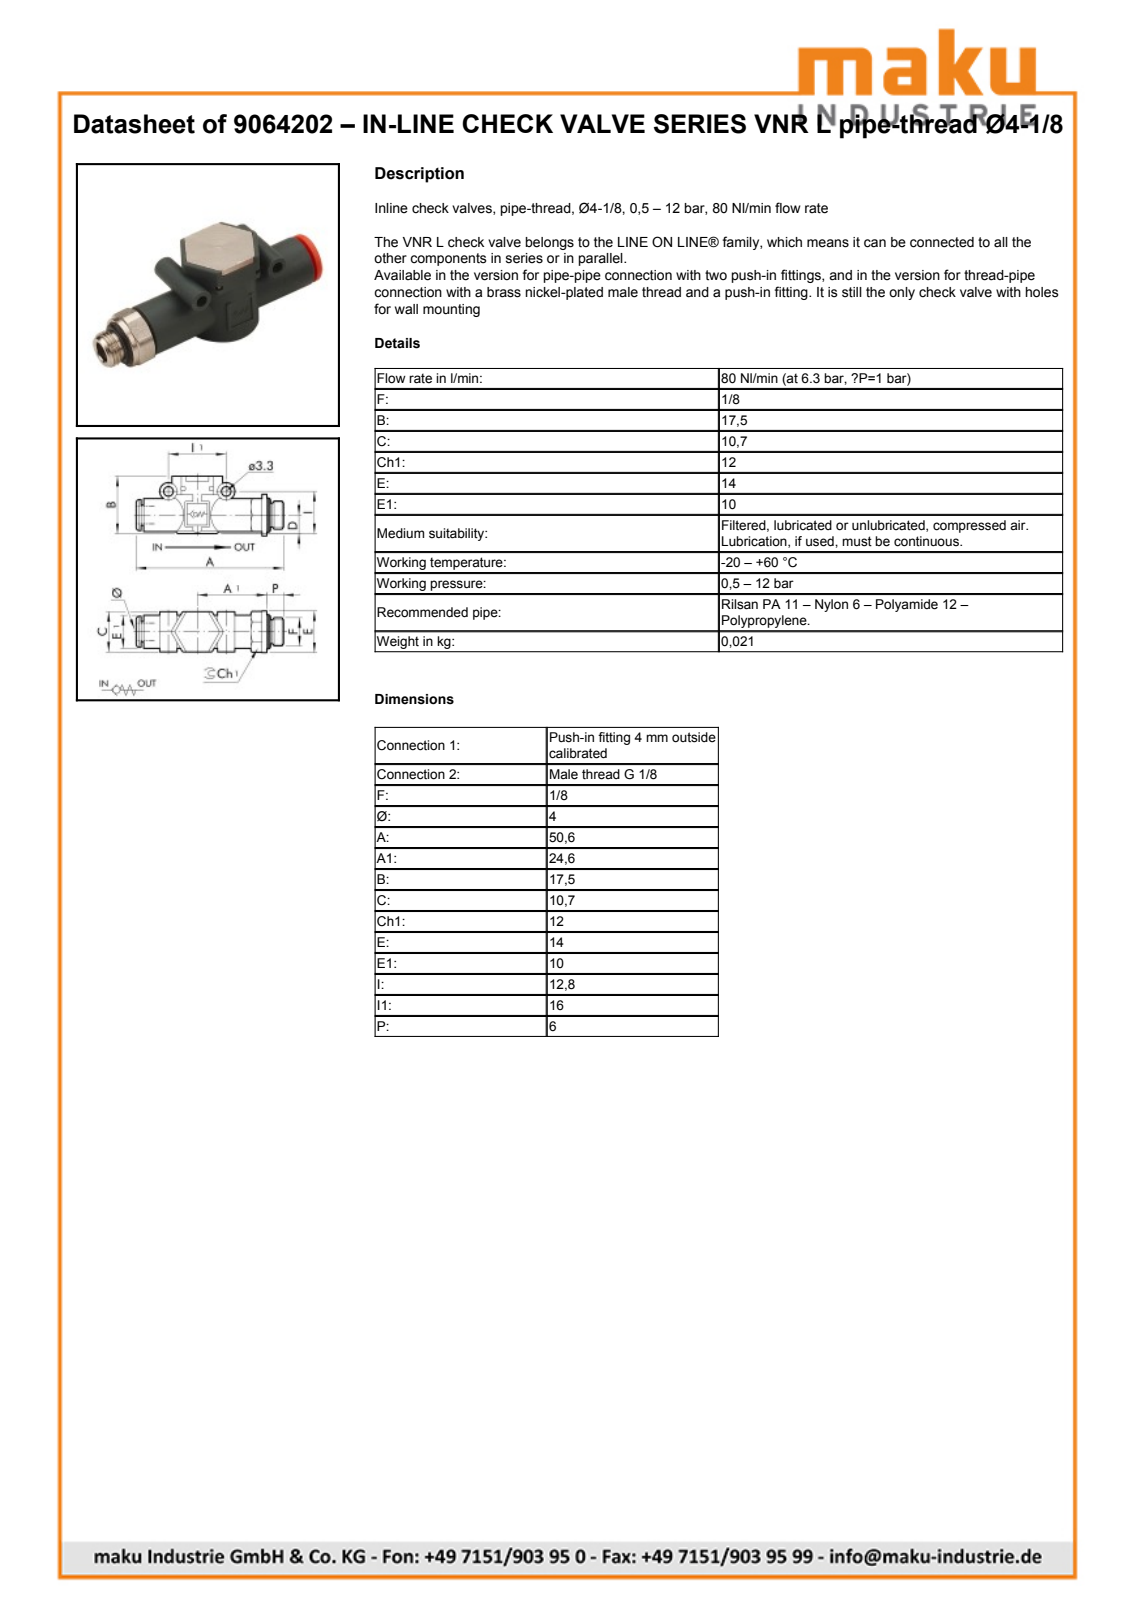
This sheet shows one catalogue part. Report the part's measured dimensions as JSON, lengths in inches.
{"part_name": "9064202; LINE-ON-LINE D4 VSR-L body; LINE-ON-LINE D4-1/8 thread port; LINE-ON-LINE D4 VNR-L bushing (+1 more)", "step_written_by": "PARTsolutions (AUTOMOTIVE_DESIGN)", "units": "inches", "bodies": {"solids": 4, "faces": 159, "planar": 95, "cylindrical": 53, "other": 11}, "overall_size": [2.024, 0.756, 0.551], "volume_in3": 0.24, "surface_area_in2": 7.469, "round_holes": [[0.13, 2], [0.142, 1], [0.157, 1], [0.161, 1], [0.197, 1], [0.236, 1], [0.252, 1], [0.256, 1], [0.295, 1], [0.307, 1], [0.319, 1]], "round_bosses_or_shafts": [[0.236, 2], [0.551, 1], [0.433, 1], [0.383, 1], [0.362, 1], [0.354, 1], [0.323, 1], [0.244, 1]], "partial_cylinders_radius": [[0.148, 1], [0.219, 1], [0.224, 1], [0.27, 1], [0.272, 1]], "face_to_face_distances": [0.402, 0.063, 0.417, 0.236, 0.413, 0.02, 0.472, 0.016, 0.634, 0.697], "hole_center_spacings": [0.424, 0.63]}
